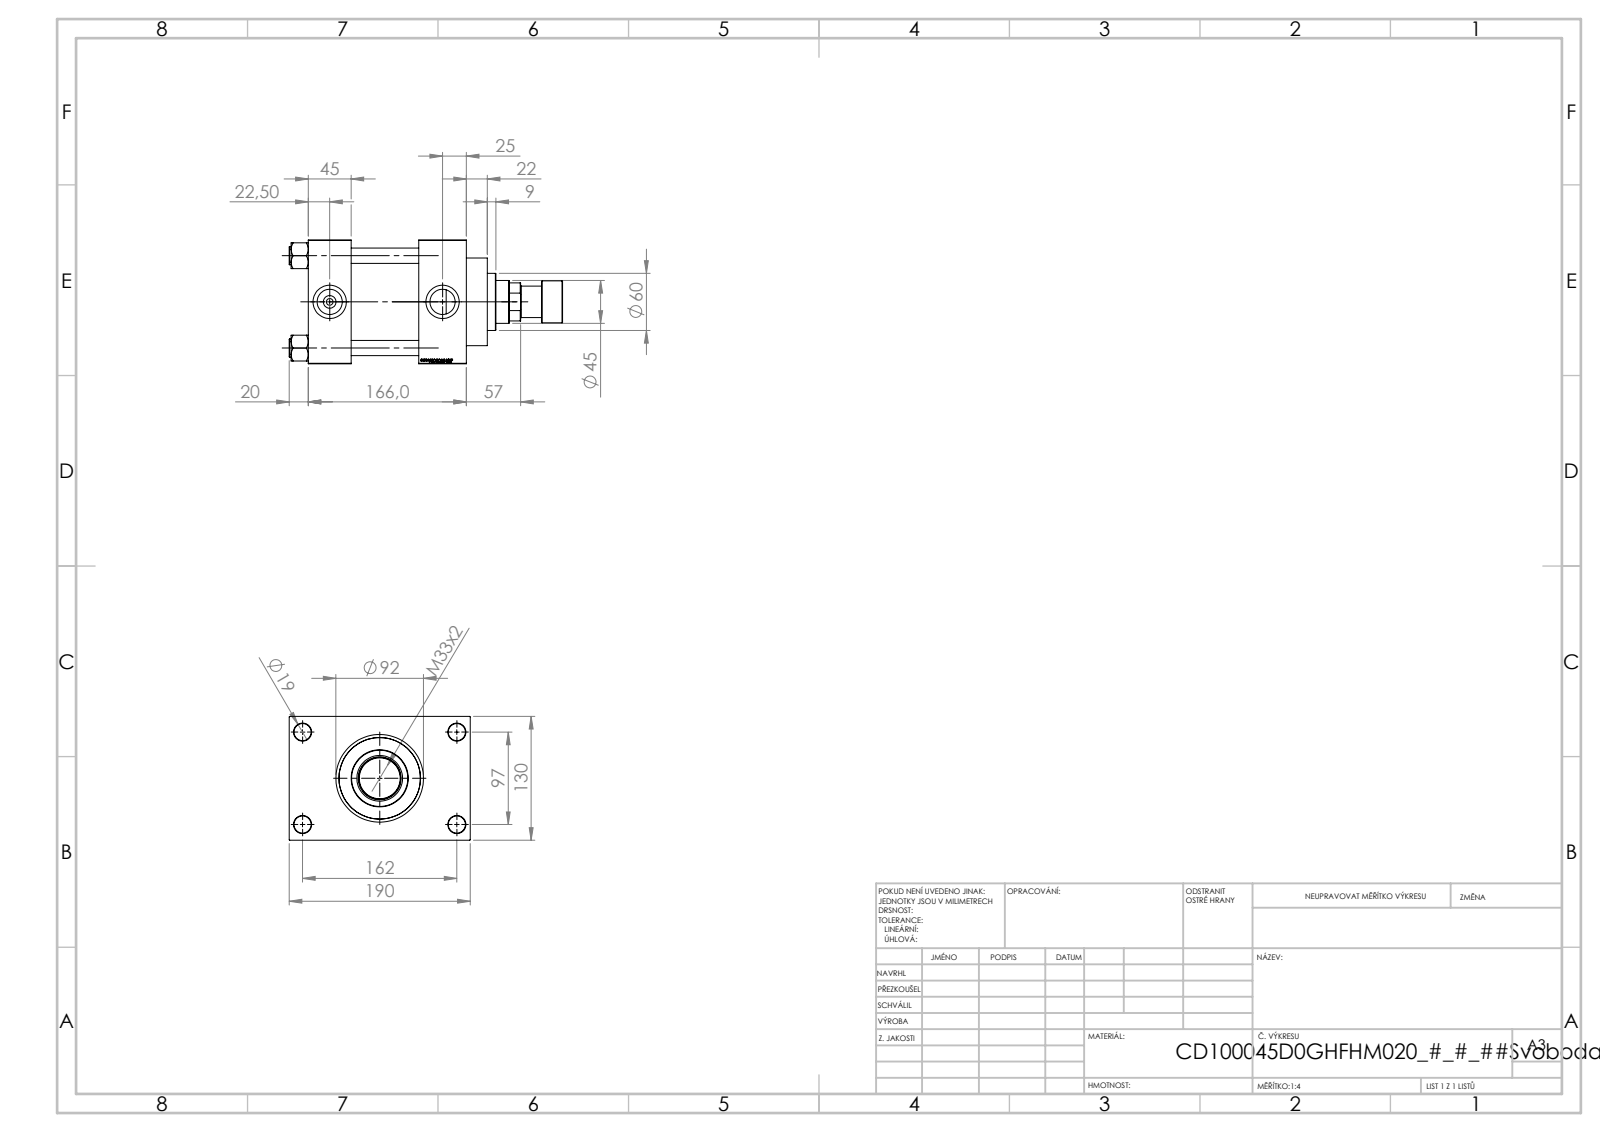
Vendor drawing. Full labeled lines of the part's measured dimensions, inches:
Part name (STEP PRODUCT): V215CR_ROD_END_F; V215CD_VCP_D; V215CD_NUT_M5_D; V215CD_D_TYCINKA (+2 more)
STEP written by: SolidWorks 2019 (CONFIG_CONTROL_DESIGN)
Units: inches
Bodies: 12 solids, 1164 faces (548 planar, 92 cylindrical, 524 other)
Overall size (bounding box): 11.299 × 7.48 × 5.118
Volume: 161.3 in³ · Surface area: 563 in²
Round holes (diameter × count): ⌀0.63 ×4, ⌀0.709 ×4, ⌀0.276 ×2, ⌀1.041 ×2, ⌀1.378 ×2, ⌀1.24 ×1, ⌀1.772 ×1, ⌀1.89 ×1, ⌀2.992 ×1, ⌀3.366 ×1, ⌀3.937 ×1
Round bosses / shafts (diameter × count): ⌀0.748 ×4, ⌀4.173 ×1, ⌀3.622 ×1, ⌀2.362 ×1, ⌀1.732 ×1, ⌀1.299 ×1
Main face-to-face distances: 5.118, 4.567, 1.772, 2.795, 6.535, 4.764, 1.969, 1.181, 6.299, 2.756
Hole centre spacings: 1.281, 2.698, 3.717, 3.815, 4.026, 5.096, 6.367, 3.819
